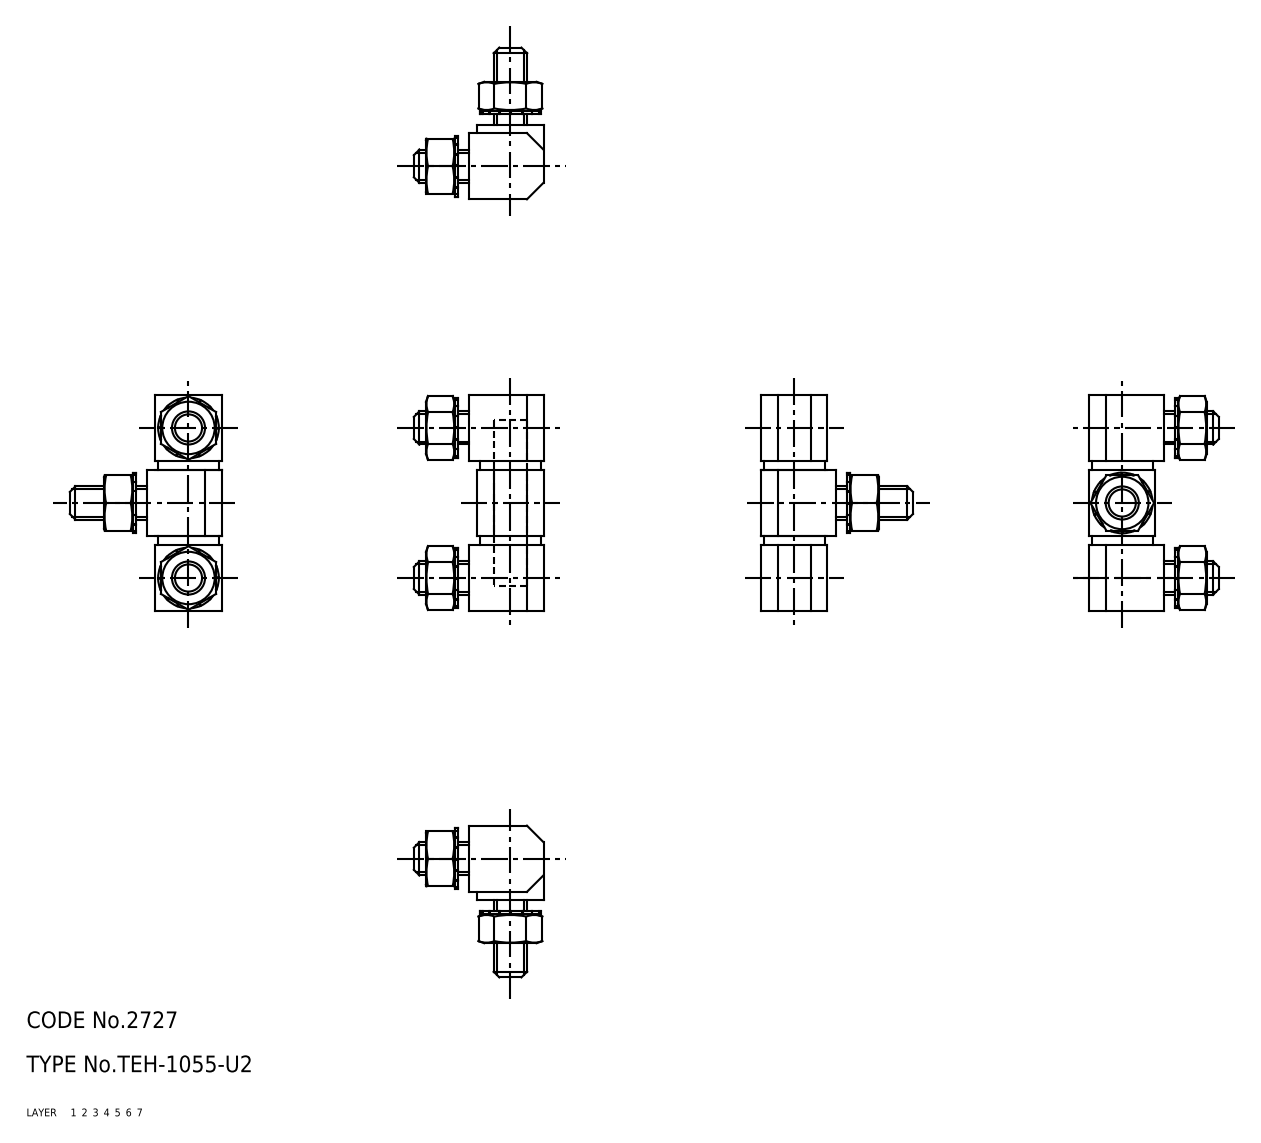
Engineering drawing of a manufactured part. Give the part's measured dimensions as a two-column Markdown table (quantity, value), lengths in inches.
| quantity | value |
| --- | --- |
| part name | washer_A; washer_B; nut; hinge pieces_A (+3 more) |
| STEP written by | CADfix (AUTOMOTIVE_DESIGN) |
| units | inches |
| bodies | 12 solids, 123 faces (0 planar, 0 cylindrical, 123 other) |
| overall size | 1.543 × 1.083 × 0.925 |
| volume | 0.47 in³ |
| surface area | 9.932 in² |
